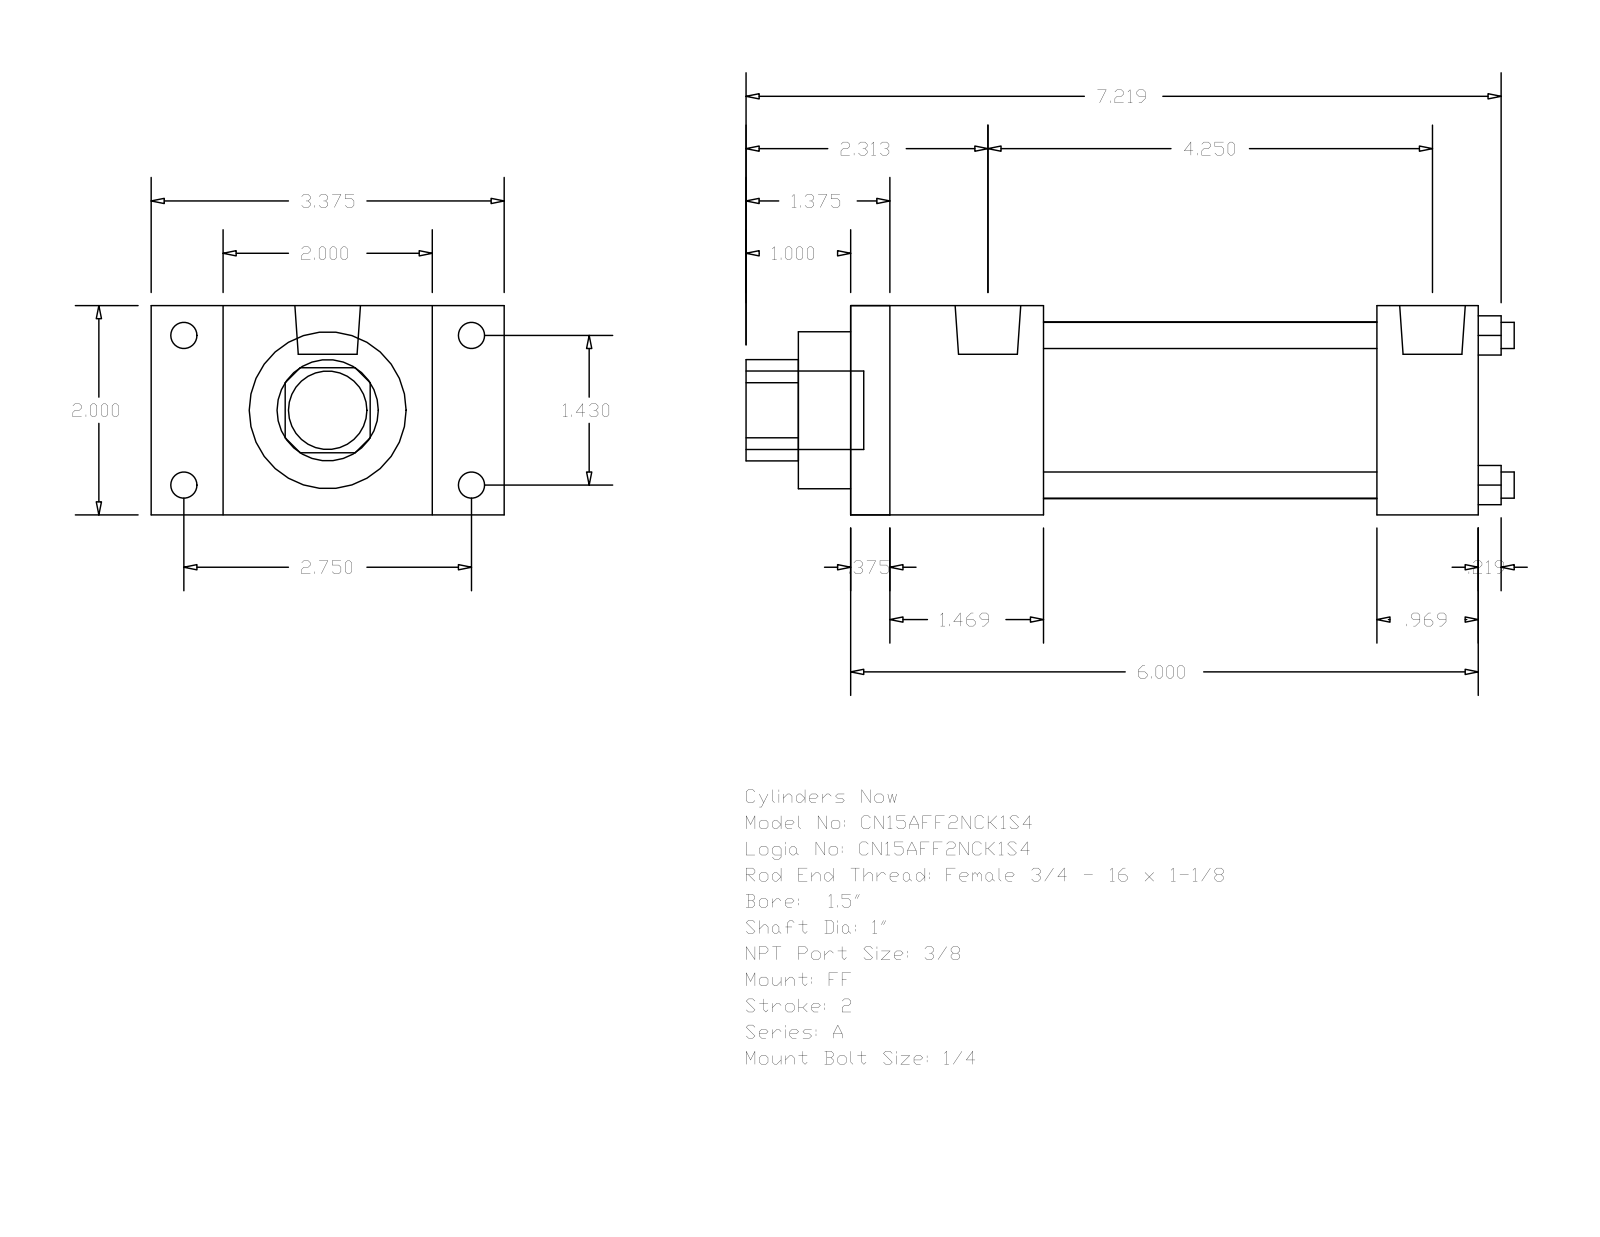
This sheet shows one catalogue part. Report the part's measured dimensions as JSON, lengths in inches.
{"part_name": "A_FF__0150_1", "step_written_by": "GSSL Pune (CONFIG_CONTROL_DESIGN)", "units": "inches", "bodies": {"solids": 0, "faces": 92, "planar": 64, "cylindrical": 28, "other": 0}, "overall_size": [7.344, 3.375, 2], "round_holes": [[0.25, 4], [1, 1], [1.5, 1], [1.69, 1]], "round_bosses_or_shafts": [[0.25, 4], [0.219, 4], [0.627, 2], [0.75, 1]], "partial_cylinders_radius": [[0.484, 1]], "face_to_face_distances": [2, 6, 0.375, 5.625, 1.844, 5.031, 1.469, 4.656, 3.187, 4.156], "hole_center_spacings": [1.011, 1.43, 2.022]}
